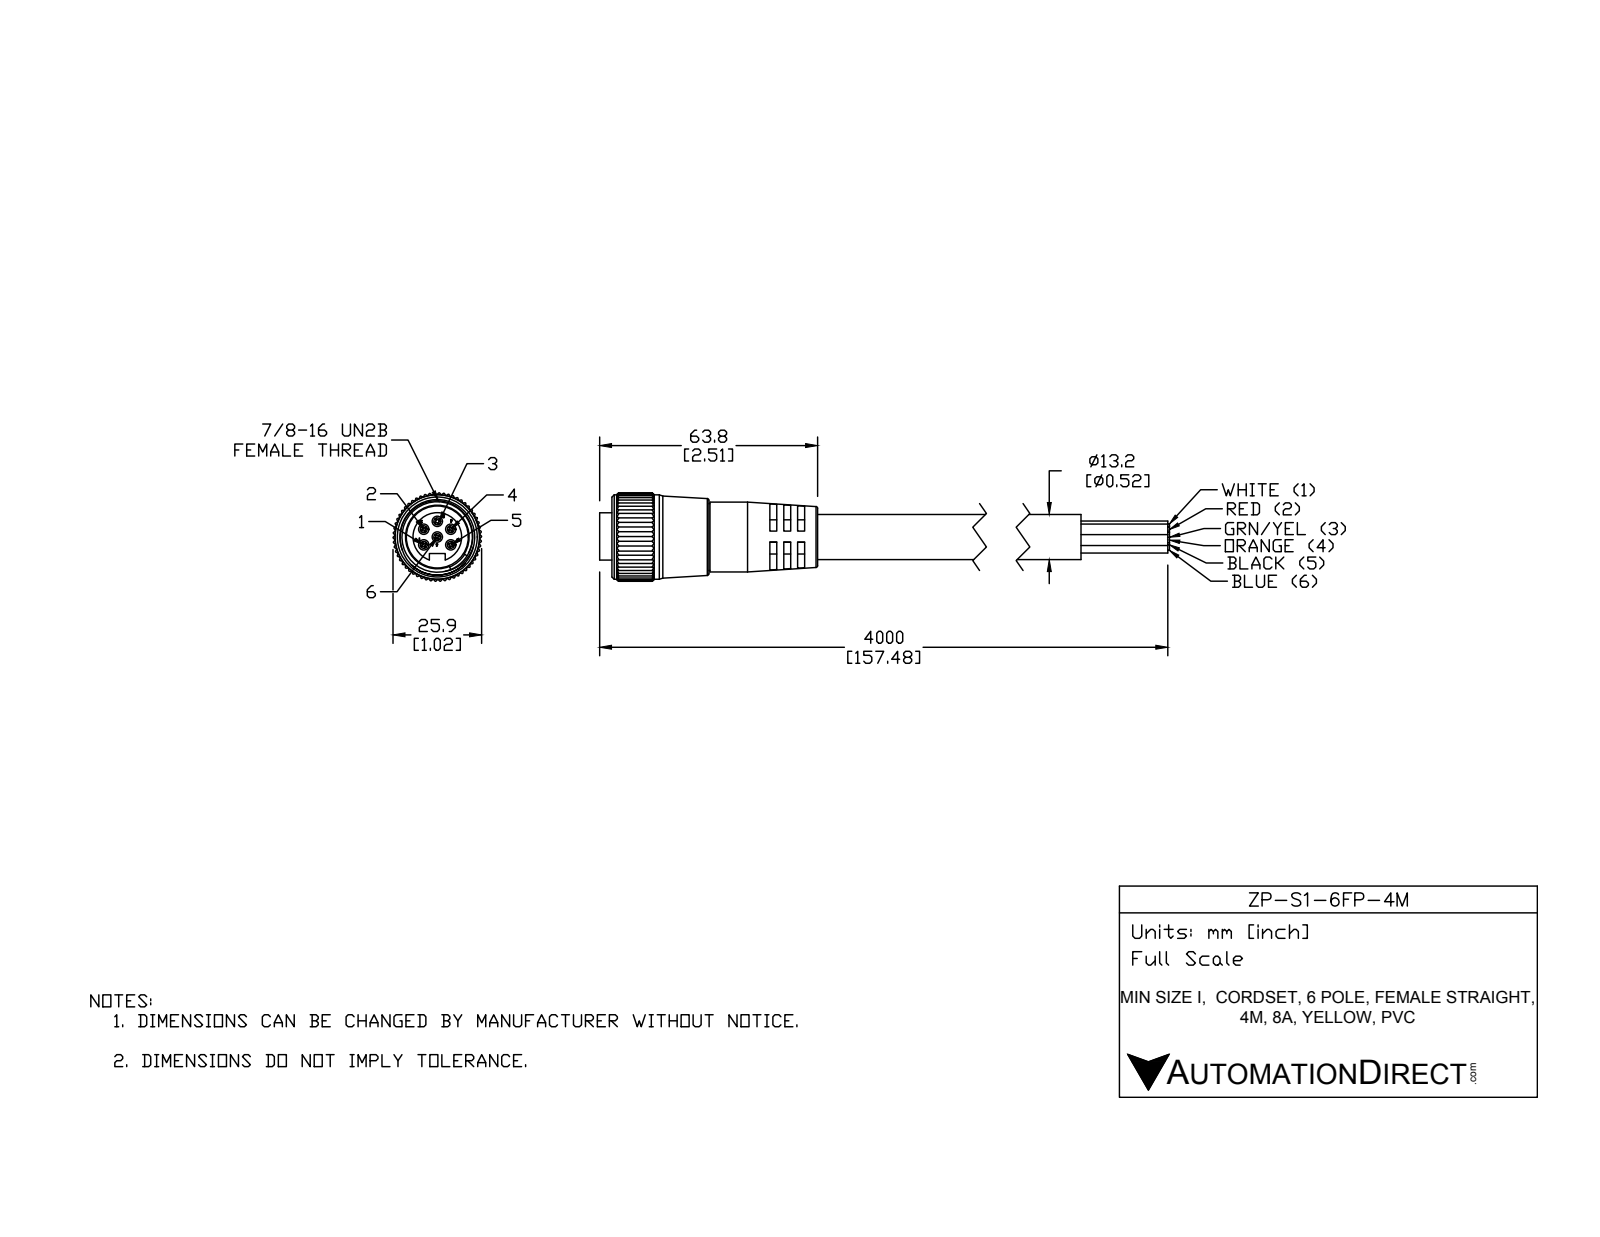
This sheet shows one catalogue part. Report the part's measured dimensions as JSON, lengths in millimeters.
{"part_name": "ZP-S1-6FP-4M", "step_written_by": "SolidWorks 2015 (AUTOMOTIVE_DESIGN)", "units": "millimeters", "bodies": {"solids": 2, "faces": 593, "planar": 222, "cylindrical": 312, "other": 59}, "overall_size": [110.36, 52.91, 25.84], "volume_mm3": 31008, "surface_area_mm2": 12592, "round_holes": [[3.05, 6], [18.14, 1], [20.58, 1], [21, 1]], "round_bosses_or_shafts": [[13.21, 2], [24.68, 1], [20.4, 1], [19.5, 1], [14.22, 1]], "partial_cylinders_radius": [[0.25, 165], [5.25, 1], [12.93, 1]], "face_to_face_distances": [4.03, 2, 2.03, 6.03, 8.06, 6.06, 21.13, 23.13, 25.16, 27.16], "hole_center_spacings": [4.57, 7.92, 4.58, 9.15]}
